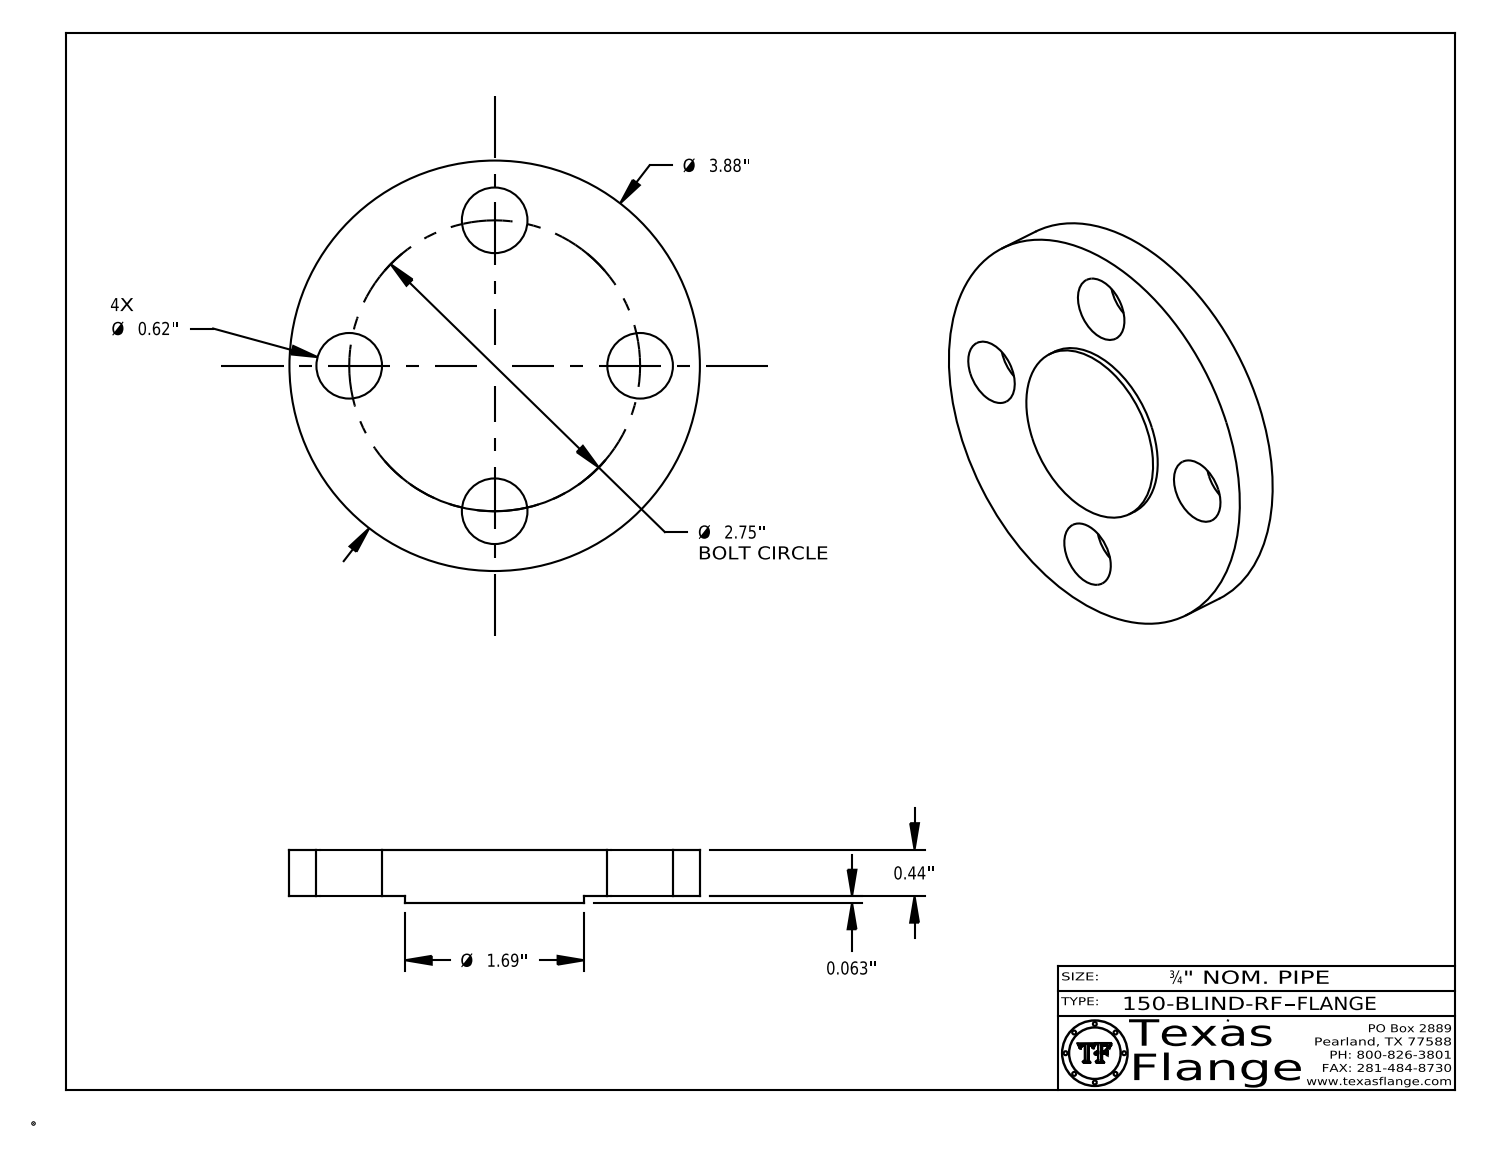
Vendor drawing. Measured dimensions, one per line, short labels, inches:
name: 150-BLIND-RF
written by: CATIA V5 STEP AP214 (AUTOMOTIVE_DESIGN)
unit: in
bodies: 1 solid, 400 faces (368 planar, 32 cylindrical, 0 other)
size: 3.88 × 3.88 × 0.503
volume: 4.81 in³; area: 30.45 in²
holes: 4× ⌀0.62, 1× ⌀0.495
bosses: 8× ⌀0.03, 1× ⌀3.88, 1× ⌀1.69, 1× ⌀0.39
face distances: 0.44, 0.063, 0.503, 0.488, 0.425, 0.015, 0.148, 0.144, 0.027, 0.122
hole spacings: 1.945, 1.052, 2.541, 2.75
